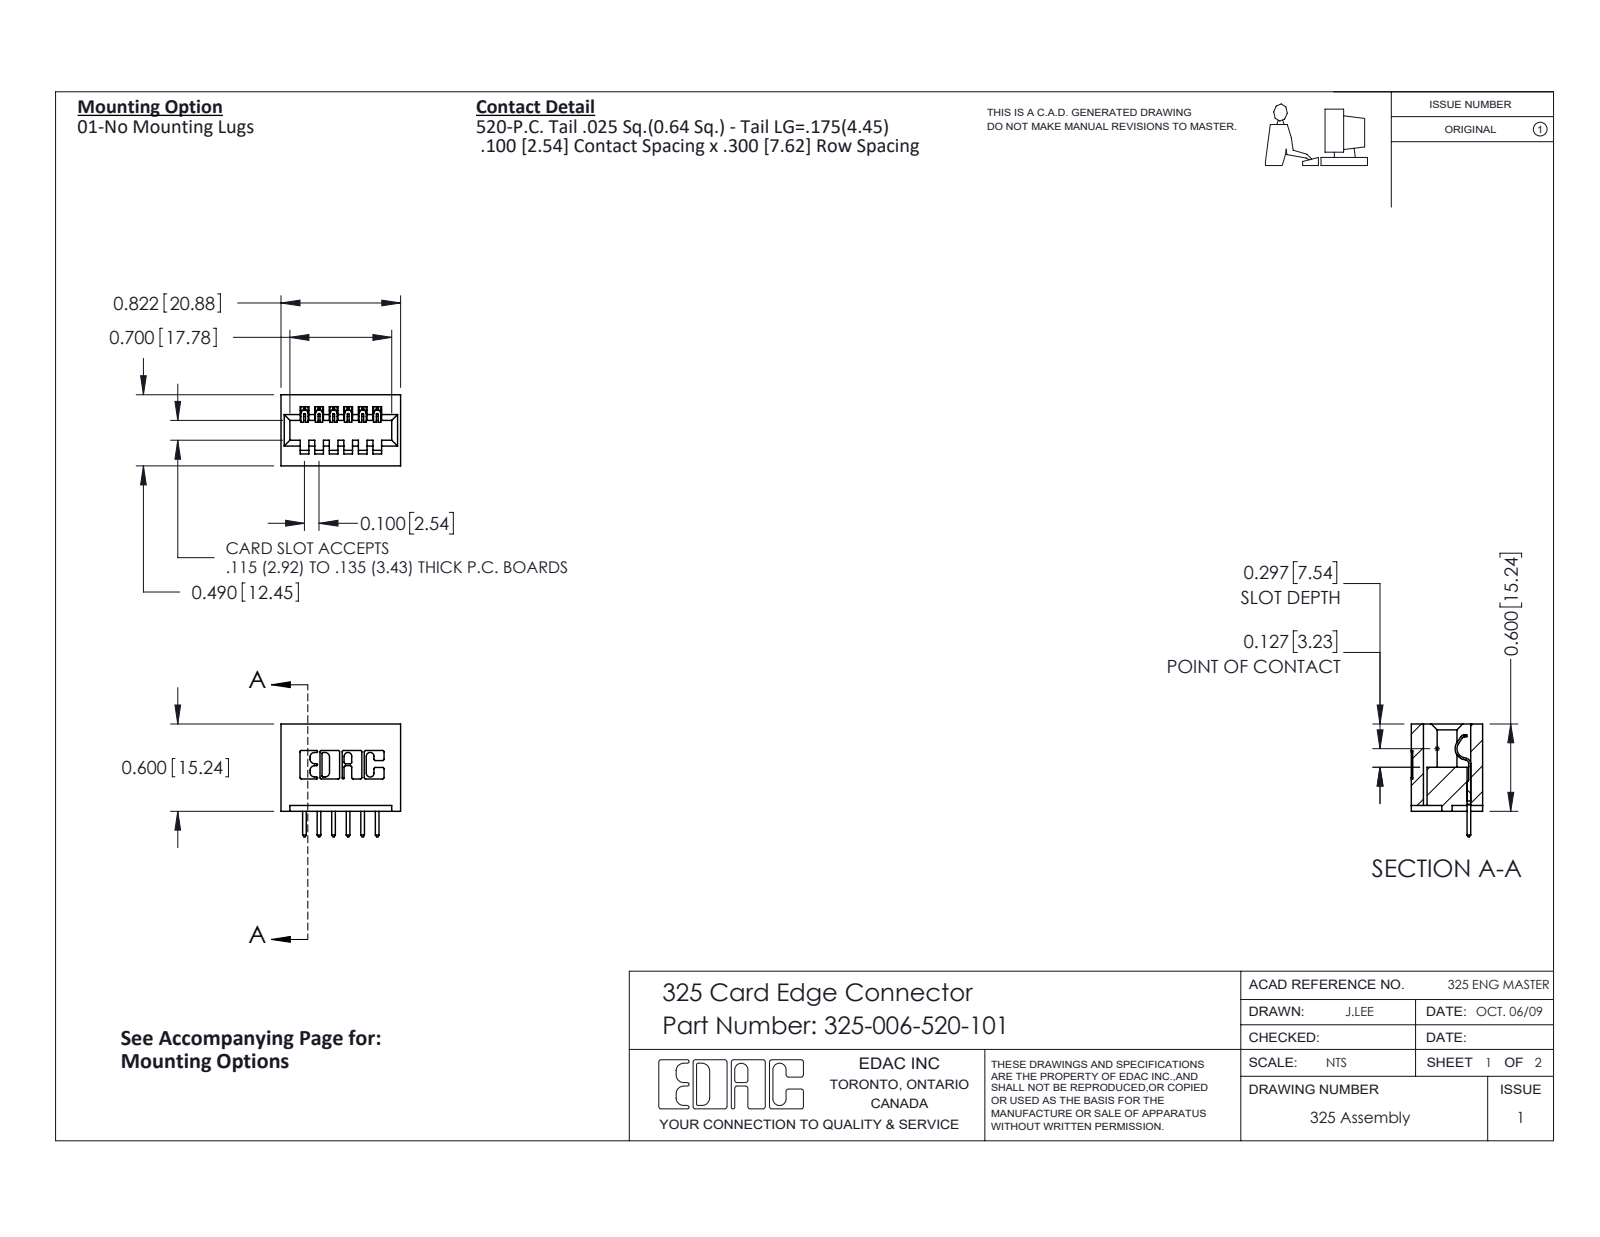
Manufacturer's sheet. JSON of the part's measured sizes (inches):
{"part_name": "325-292-001_325-293-120; 325-006-520-101; 325 Part_Lugless", "step_written_by": "SolidWorks 2016 (CONFIG_CONTROL_DESIGN)", "units": "inches", "bodies": {"solids": 7, "faces": 454, "planar": 318, "cylindrical": 136, "other": 0}, "overall_size": [0.822, 0.775, 0.49], "volume_in3": 0.178, "surface_area_in2": 4.666, "partial_cylinders_radius": [[0.01, 22], [0.006, 12], [0.01, 12], [0.007, 6], [0.031, 6], [0.026, 3], [0.014, 1], [0.022, 1]], "face_to_face_distances": [0.1, 0.3, 0.2, 0.083, 0.407, 0.04, 0.06, 0.49, 0.16, 0.822]}
